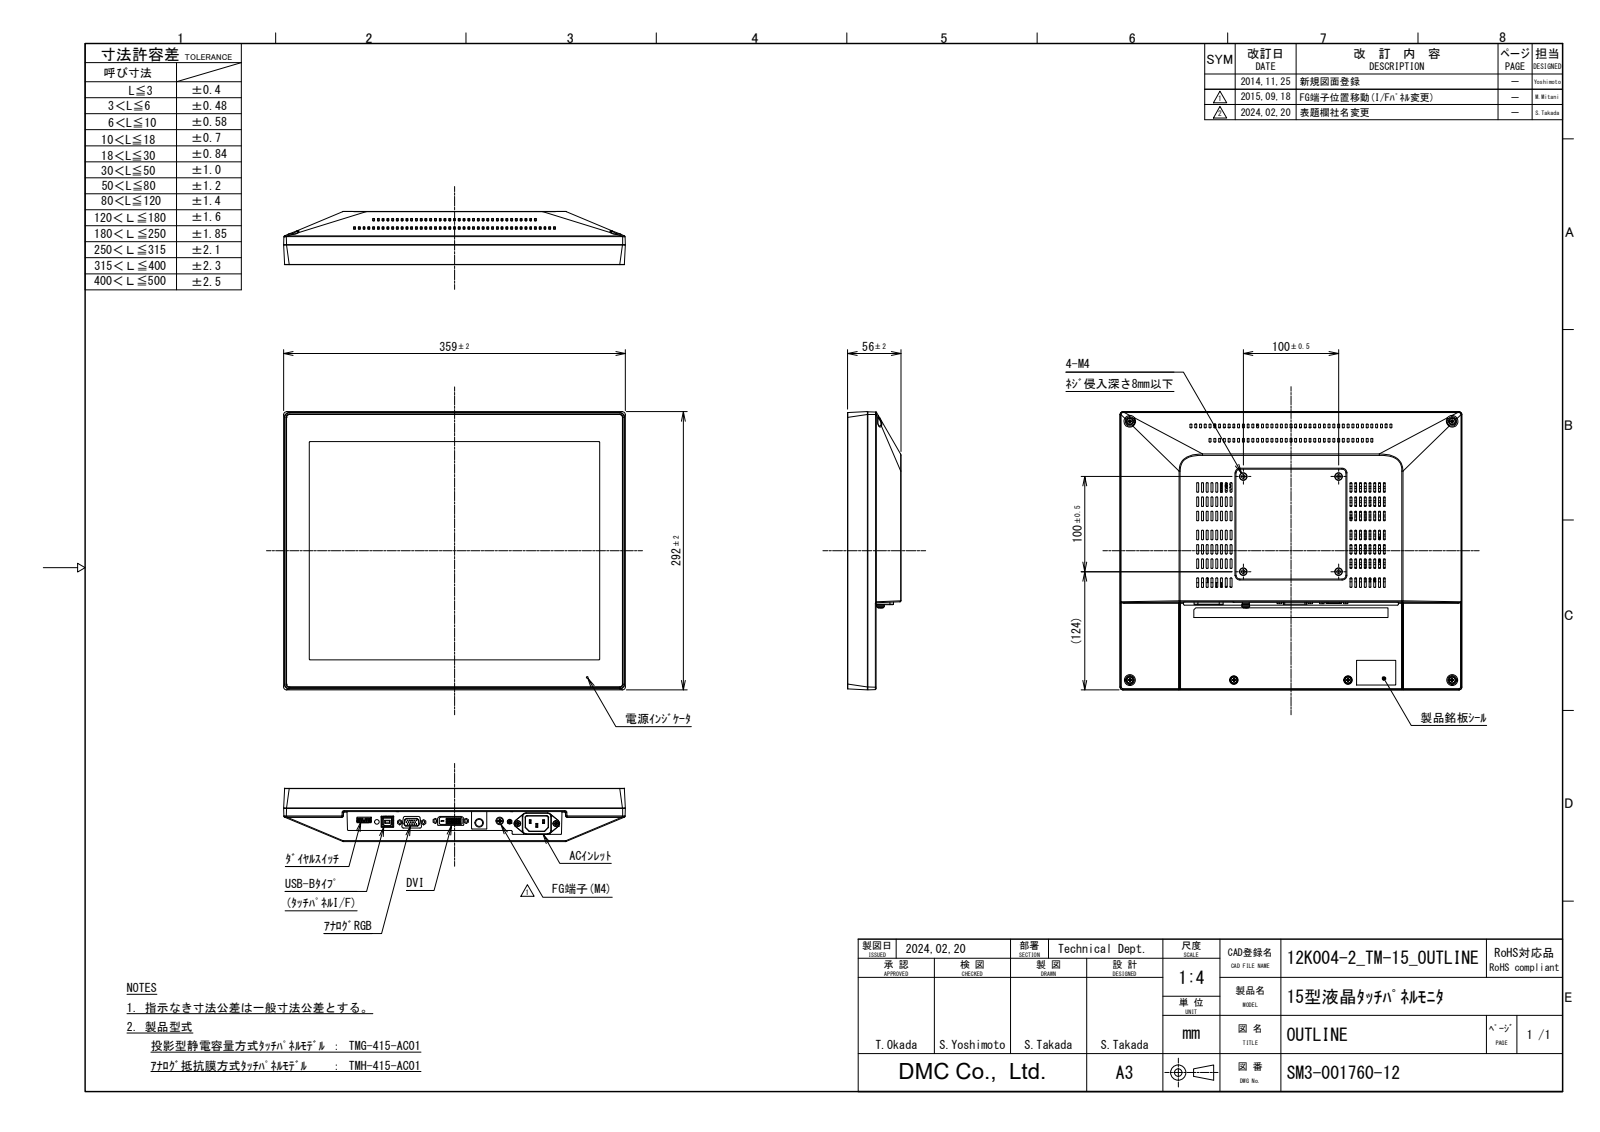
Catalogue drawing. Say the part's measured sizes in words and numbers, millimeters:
The part is named "HP_TMG(H)-415-AC01". Its 3-D file was written by "Autodesk Inventor 2017 (CONFIG_CONTROL_DESIGN)". It is 1 solid with 5668 faces: 2948 planar, 1162 cylindrical and 1558 other. Overall it measures 359 by 292 by 56 millimeters. Its volume is 831 987 cubic millimeters and its surface area 911 571 square millimeters. Round holes: 123 of diameter 3.5, 34 of diameter 8, 24 of diameter 2.46, 24 of diameter 4, 17 of diameter 1, 13 of diameter 3, 12 of diameter 3.2, 4 of diameter 2.01, 4 of diameter 4.8, 4 of diameter 9, 4 of diameter 10, 2 of diameter 2.6. Round bosses or shafts: 20 of diameter 6.15, 14 of diameter 3, 12 of diameter 3.6, 5 of diameter 7.15, 5 of diameter 4, 4 of diameter 4.18, 4 of diameter 4.1, 4 of diameter 0.8. Partial cylindrical surfaces (rounded edges, fillets, slot ends): 135 of radius 0.5, 113 of radius 1, 30 of radius 0.3, 18 of radius 1.3, 13 of radius 0.1, 13 of radius 2, 12 of radius 1.6, 10 of radius 3. The main face-to-face distances are 1, 3, 20.61, 19.61, 19.51, 18.51, 1.1, 27.7, 18.5, 26. The hole center spacings are 5, 2.29, 11.18, 10, 15.81, 7.07, 15, 3.96.
